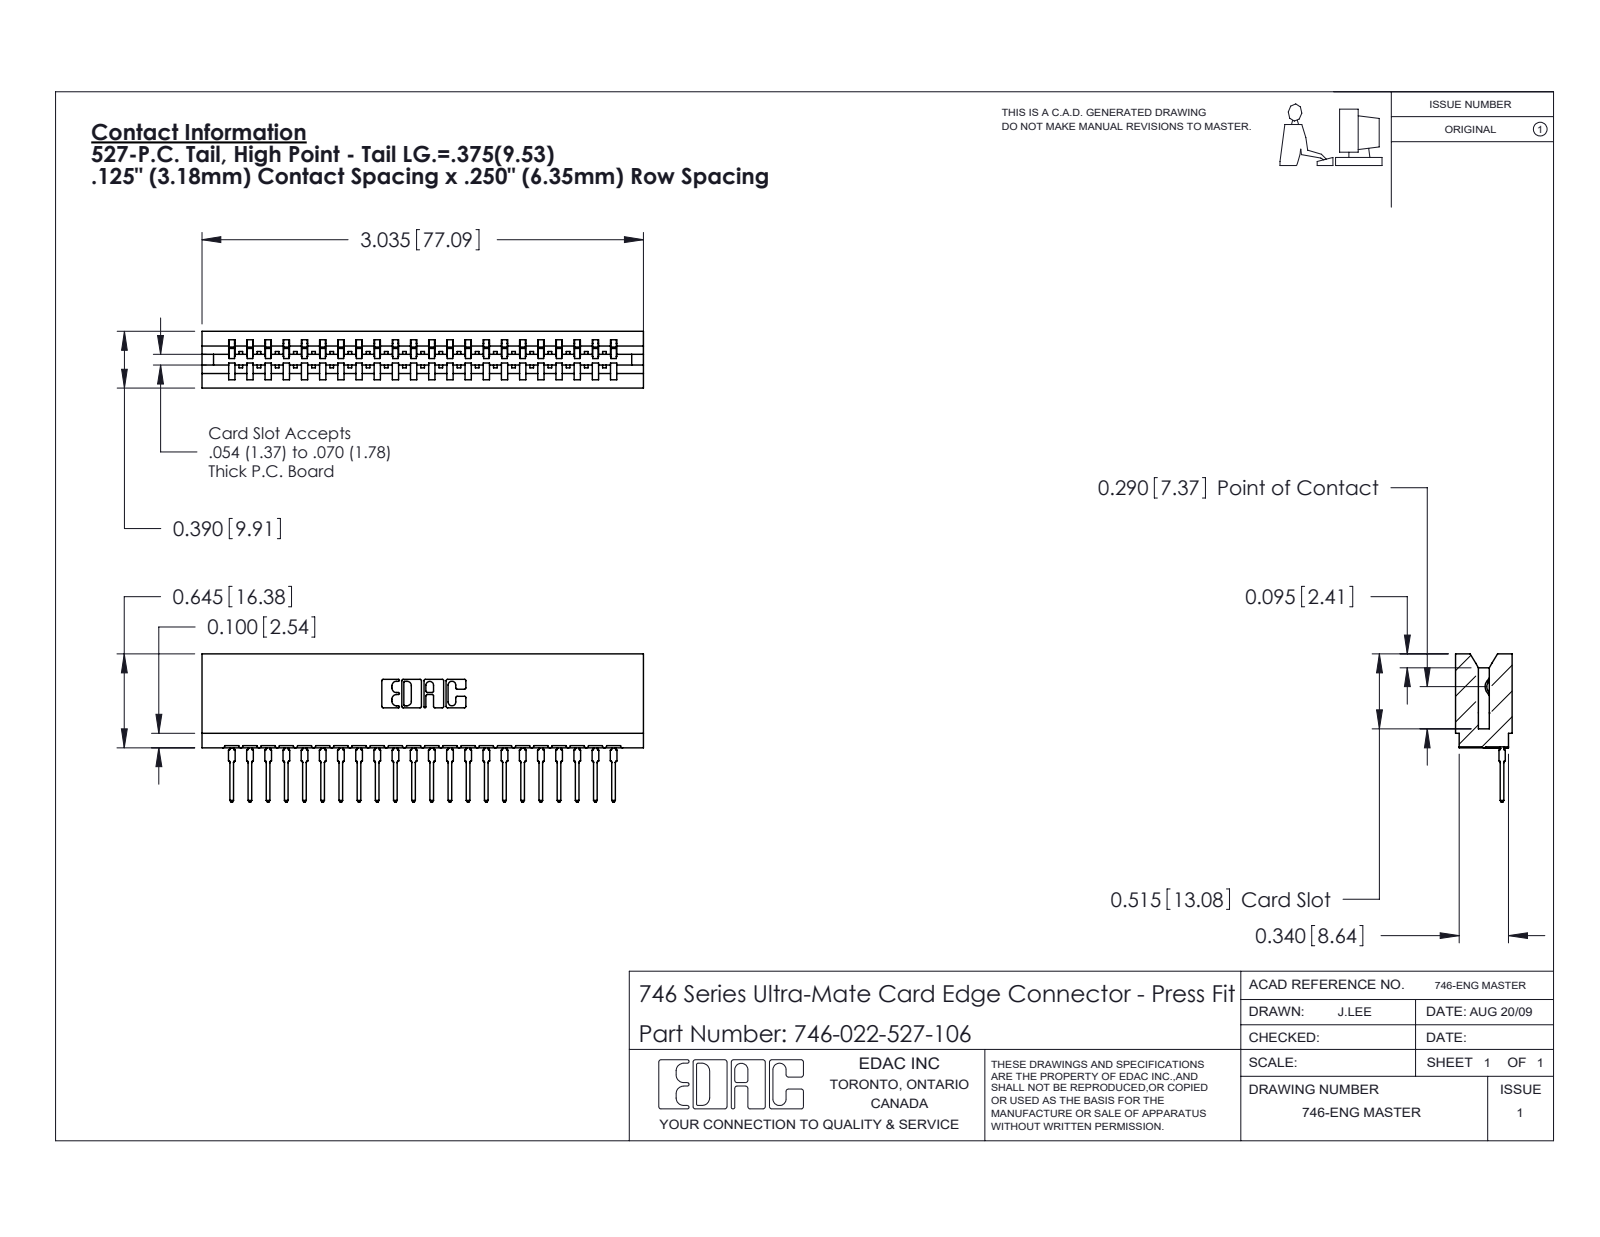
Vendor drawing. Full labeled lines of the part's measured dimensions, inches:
Part name (STEP PRODUCT): 746 Part_.515 Slot Depth - 06; 746-292-001_527; 746-022-527-106
STEP written by: SolidWorks 2020 (CONFIG_CONTROL_DESIGN)
Units: inches
Bodies: 23 solids, 2474 faces (1442 planar, 460 cylindrical, 572 other)
Overall size (bounding box): 3.035 × 1.019 × 0.39
Volume: 0.5 in³ · Surface area: 18.51 in²
Partial cylindrical surfaces — rounded edges, fillets, slot ends (radius × count): R0.021 ×44, R0.015 ×23, R0.01 ×22, R0.007 ×6, R0.031 ×6, R0.005 ×4, R0.011 ×4, R0.026 ×3
Main face-to-face distances: 0.333, 0.057, 0.25, 0.39, 0.5, 0.025, 0.307, 0.042, 0.083, 0.125
